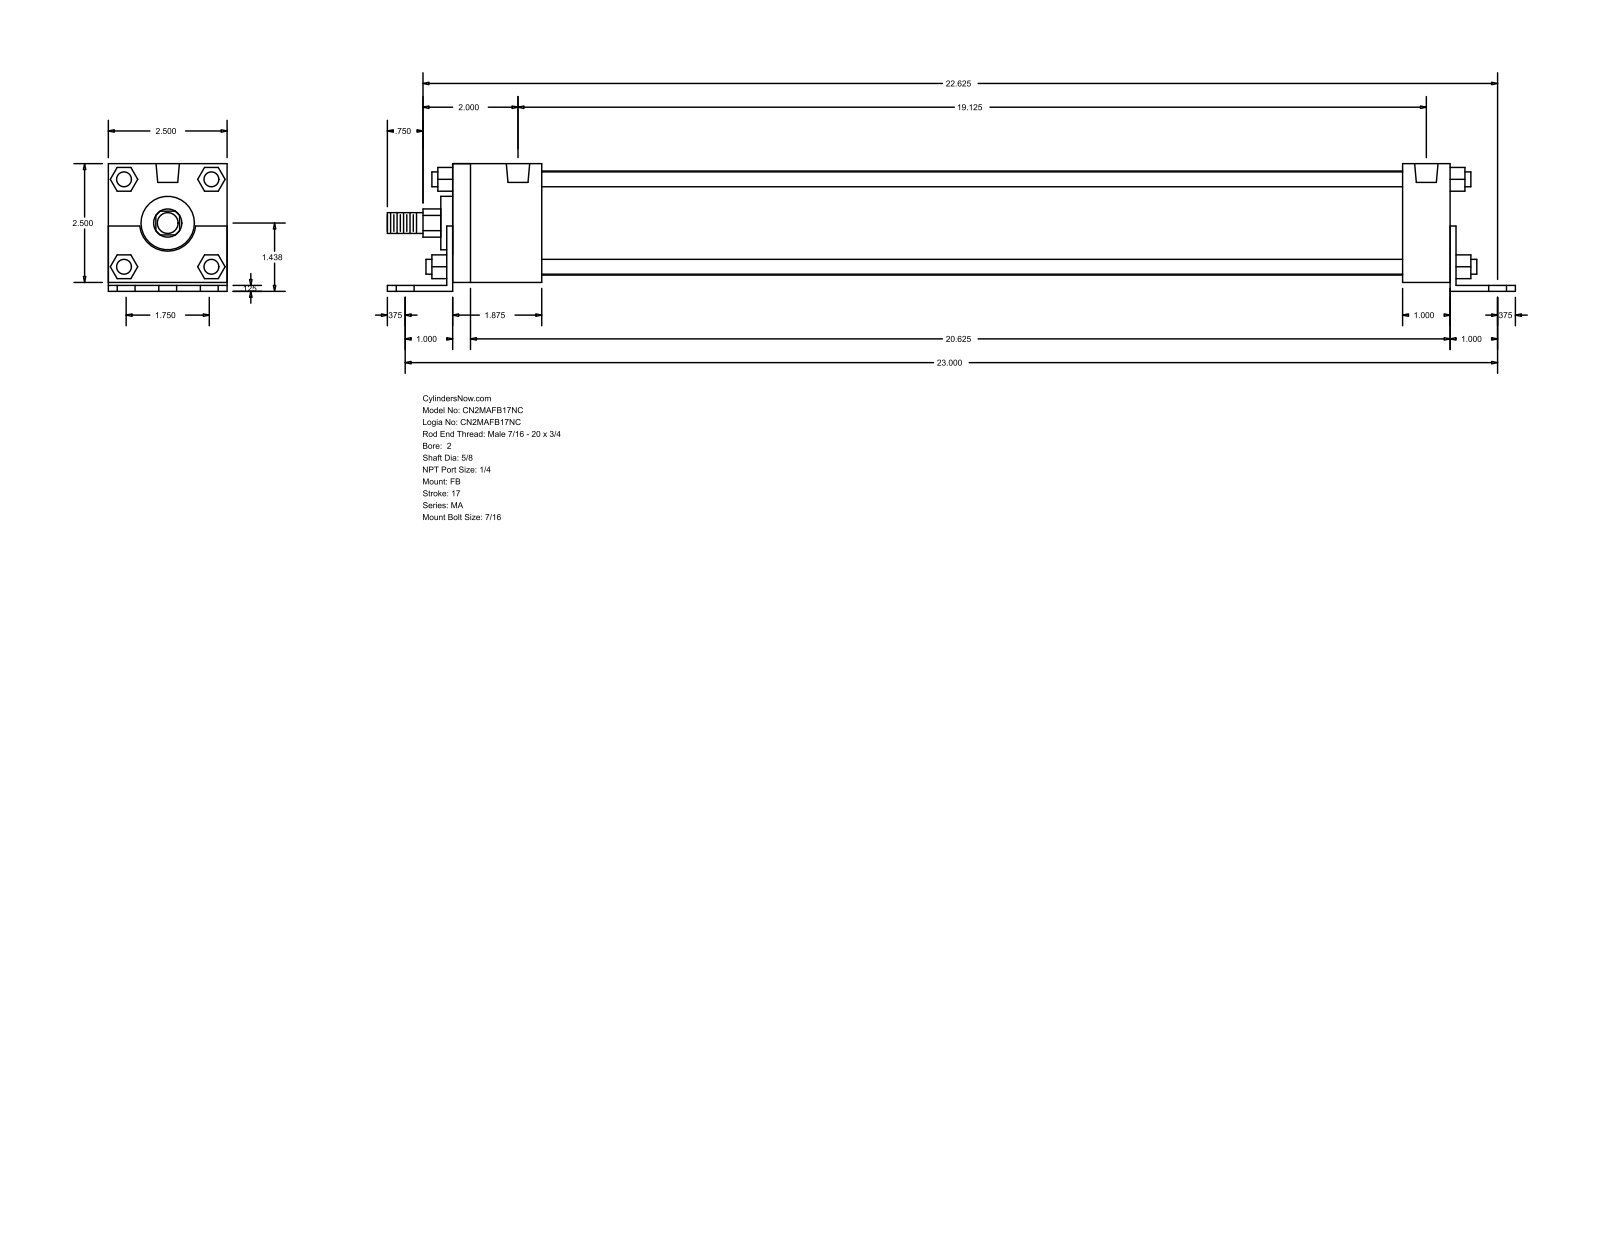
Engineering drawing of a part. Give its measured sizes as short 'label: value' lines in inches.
name: MA_FB__0200_0.625
written by: GSSL Pune (CONFIG_CONTROL_DESIGN)
unit: in
bodies: 0 solids, 140 faces (105 planar, 35 cylindrical, 0 other)
size: 23.75 × 2.687 × 2.5
holes: 6× ⌀0.437, 4× ⌀0.313, 2× ⌀0.492
bosses: 4× ⌀0.313, 1× ⌀2.19, 1× ⌀1.125, 1× ⌀0.625, 1× ⌀0.437
rounds: 1× R0.297, 1× R0.593
face distances: 2.5, 0.187, 0.125, 2.687, 0.063, 0.125, 2.563, 21.125, 21, 0.5
hole spacings: 0.875, 23.017, 23, 1.736, 1.75, 2.531, 19.125, 20.643
